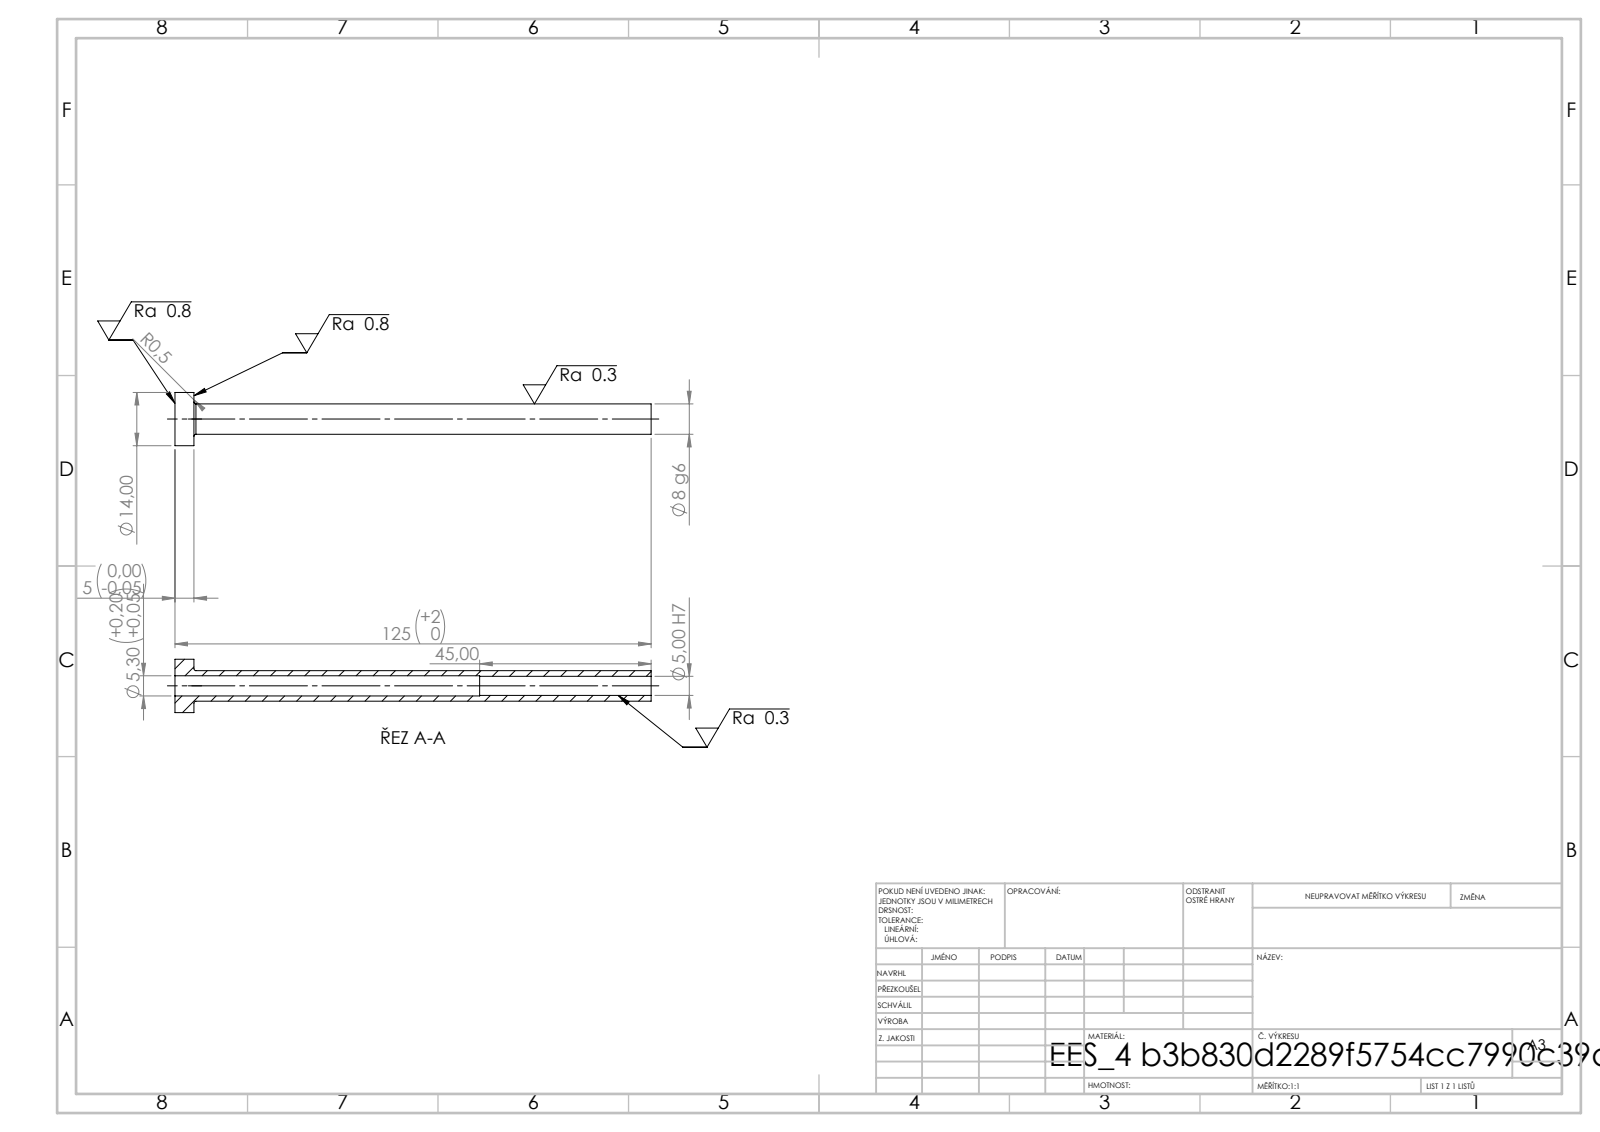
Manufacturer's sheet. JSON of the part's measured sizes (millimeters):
{"step_written_by": "SolidWorks 2019 (CONFIG_CONTROL_DESIGN)", "units": "millimeters", "bodies": {"solids": 1, "faces": 14, "planar": 4, "cylindrical": 8, "other": 2}, "overall_size": [125, 14, 14], "volume_mm3": 4154, "surface_area_mm2": 5538, "round_holes": [[5, 1], [5.3, 1]], "round_bosses_or_shafts": [[14, 1], [8, 1]], "face_to_face_distances": [5, 125, 120, 80, 75, 45]}
